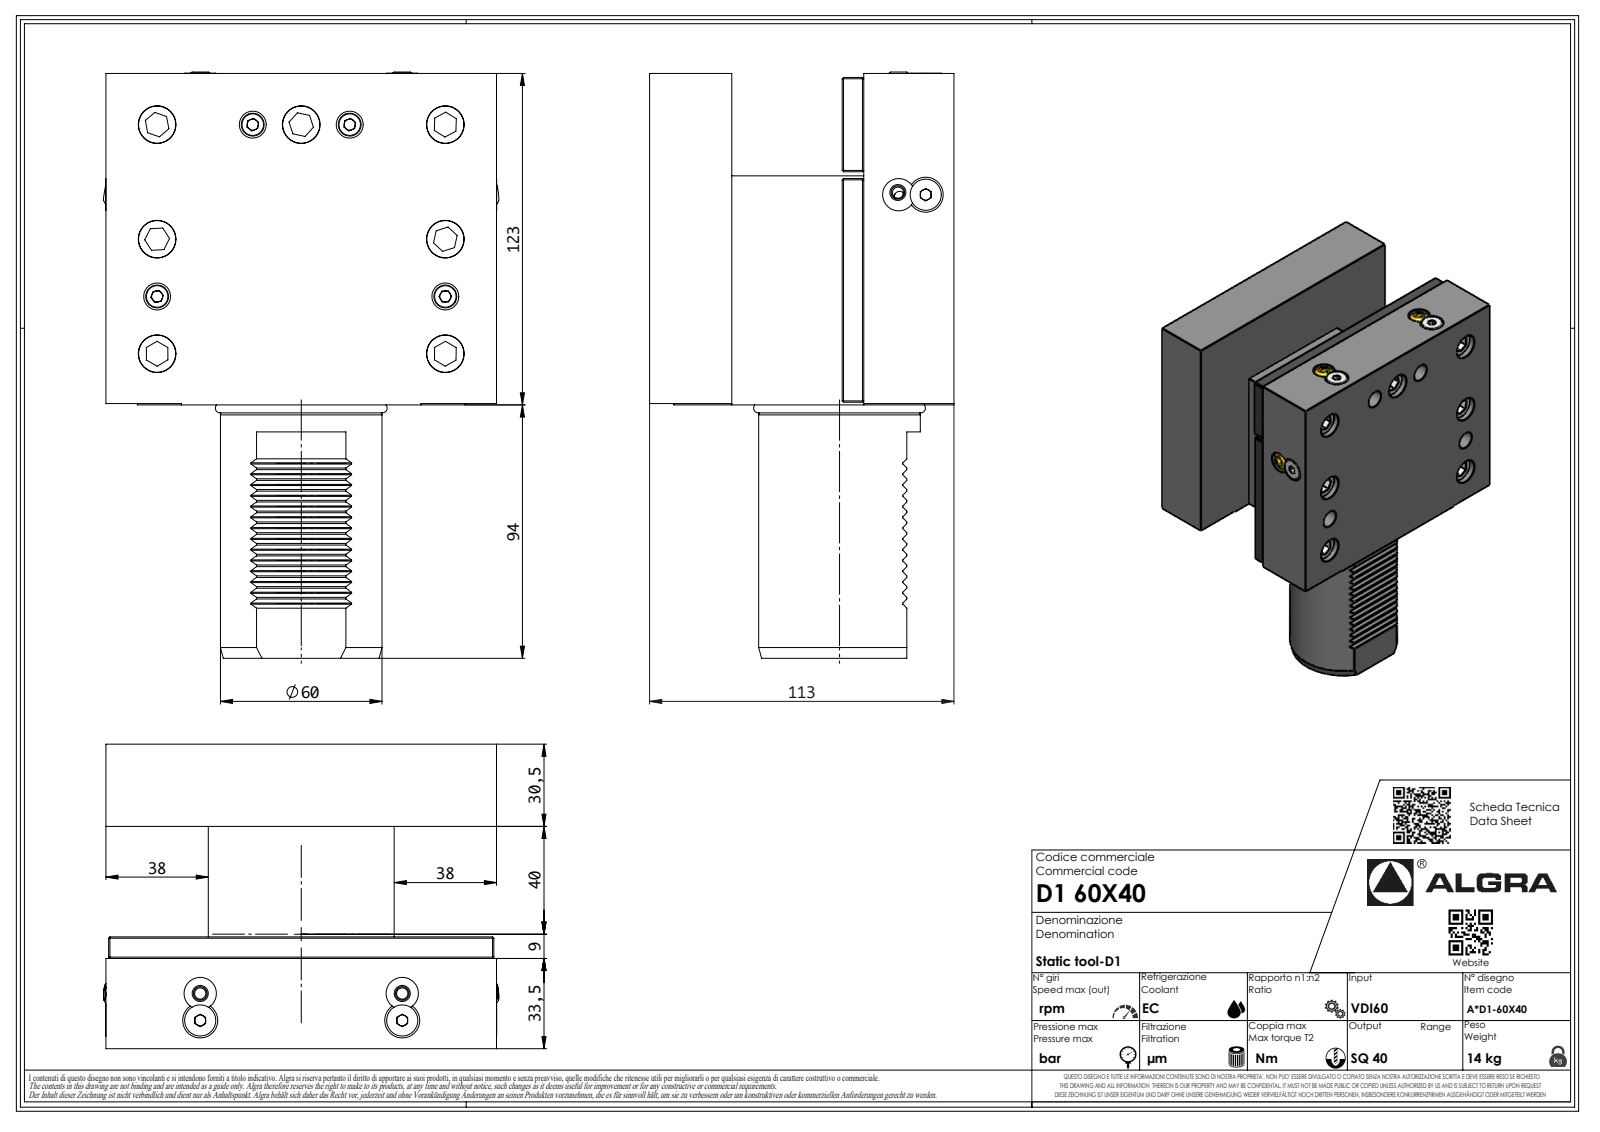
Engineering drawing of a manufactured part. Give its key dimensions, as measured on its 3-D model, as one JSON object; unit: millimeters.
{"part_name": "D160X40", "step_written_by": "SolidWorks 2023 (AUTOMOTIVE_DESIGN)", "units": "millimeters", "bodies": {"solids": 1, "faces": 367, "planar": 277, "cylindrical": 45, "other": 45}, "overall_size": [217, 145, 113], "volume_mm3": 1767000, "surface_area_mm2": 134054, "round_holes": [[2.1, 1]], "round_bosses_or_shafts": [[60, 1], [58.7, 1], [6.37, 1], [1.7, 1]], "partial_cylinders_radius": [[0.3, 14], [0.33, 7], [0.52, 7], [3.7, 7], [0.21, 1], [61.5, 1]], "face_to_face_distances": [113, 30.5, 82.5, 38, 41, 71.5, 41.5, 107, 145, 0.5]}
